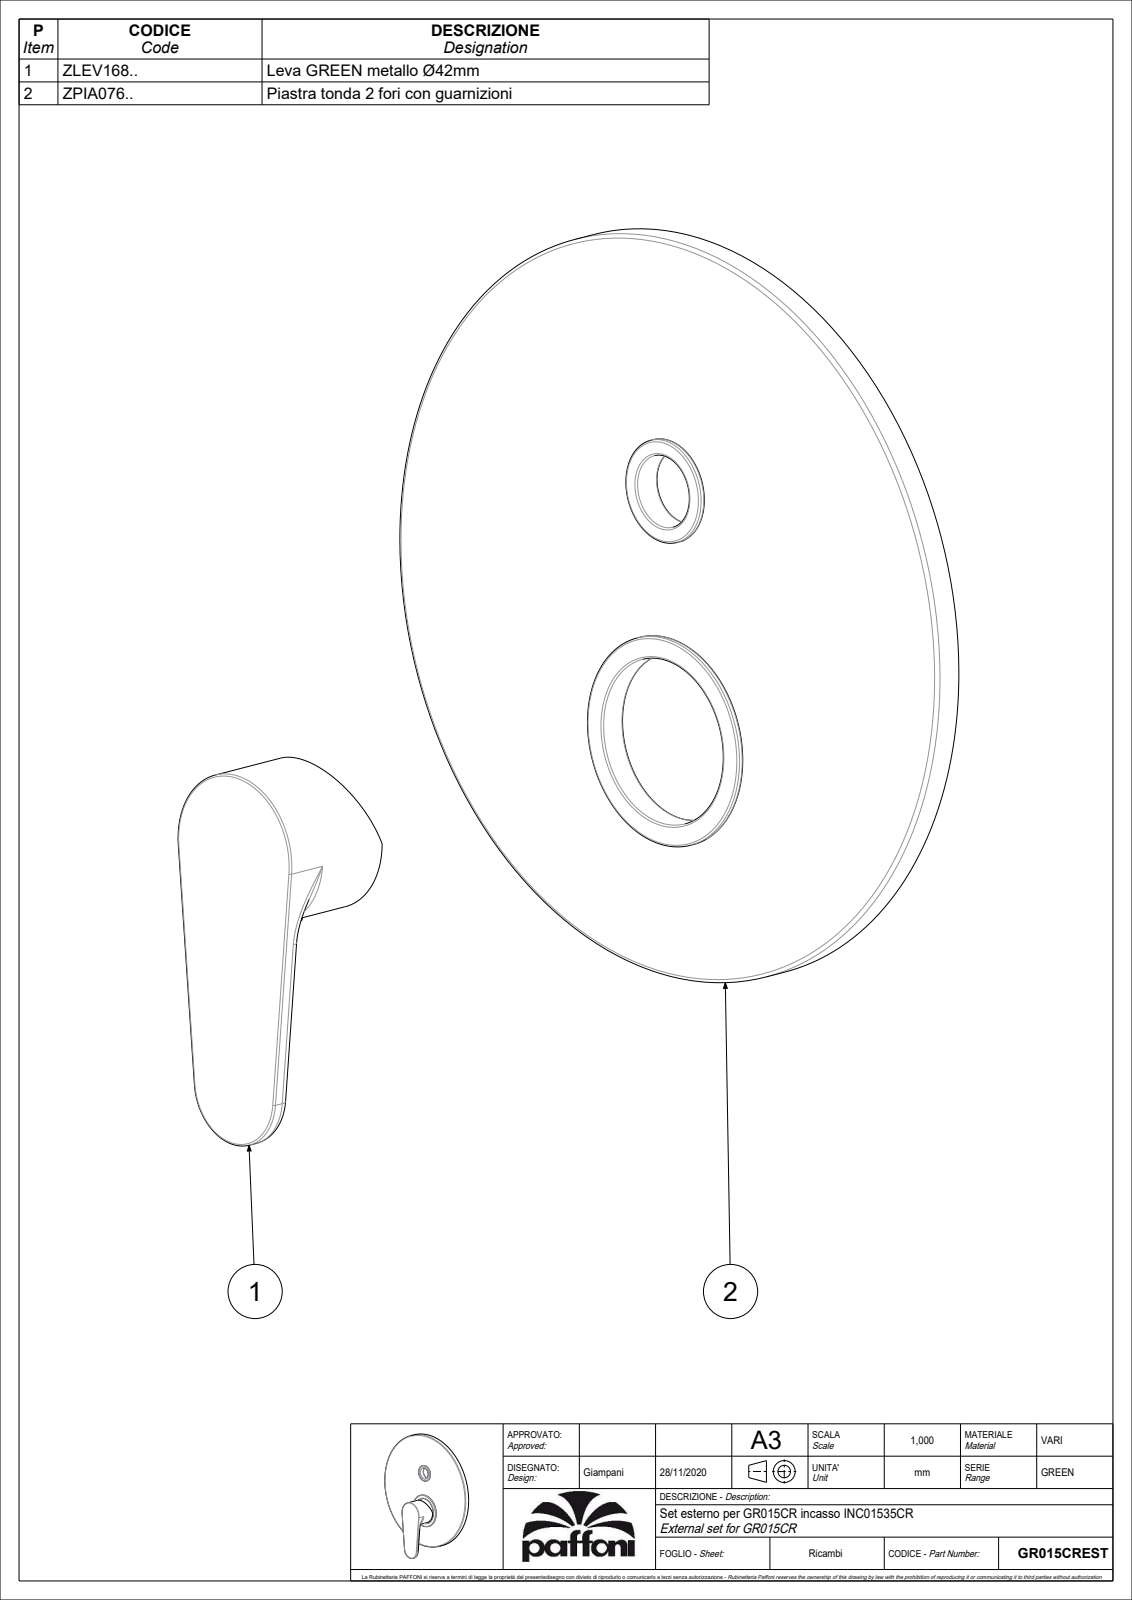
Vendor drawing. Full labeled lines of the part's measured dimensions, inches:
Part name (STEP PRODUCT): GR015CREST
STEP written by: CREO PARAMETRIC BY PTC INC, 2020044 (CONFIG_CONTROL_DESIGN)
Units: inches
Bodies: 2 solids, 157 faces (59 planar, 53 cylindrical, 45 other)
Overall size (bounding box): 8.476 × 7.874 × 1.772
Volume: 10.29 in³ · Surface area: 150.3 in²
Round holes (diameter × count): ⌀0.118 ×1, ⌀0.165 ×1, ⌀0.752 ×1, ⌀1.535 ×1, ⌀1.756 ×1, ⌀1.969 ×1, ⌀5.709 ×1, ⌀7.795 ×1
Round bosses / shafts (diameter × count): ⌀7.874 ×1, ⌀7.677 ×1, ⌀2.213 ×1, ⌀1.965 ×1, ⌀1.654 ×1, ⌀0.988 ×1, ⌀0.925 ×1, ⌀0.299 ×1
Partial cylindrical surfaces — rounded edges, fillets, slot ends (radius × count): R0.02 ×2, R0.118 ×2, R0.591 ×1
Main face-to-face distances: 0.039, 0.315, 0.354, 1.772, 1.457, 1.417, 0.236, 1.535, 1.22, 1.181
Hole centre spacings: 1.268, 1.409, 2.677
